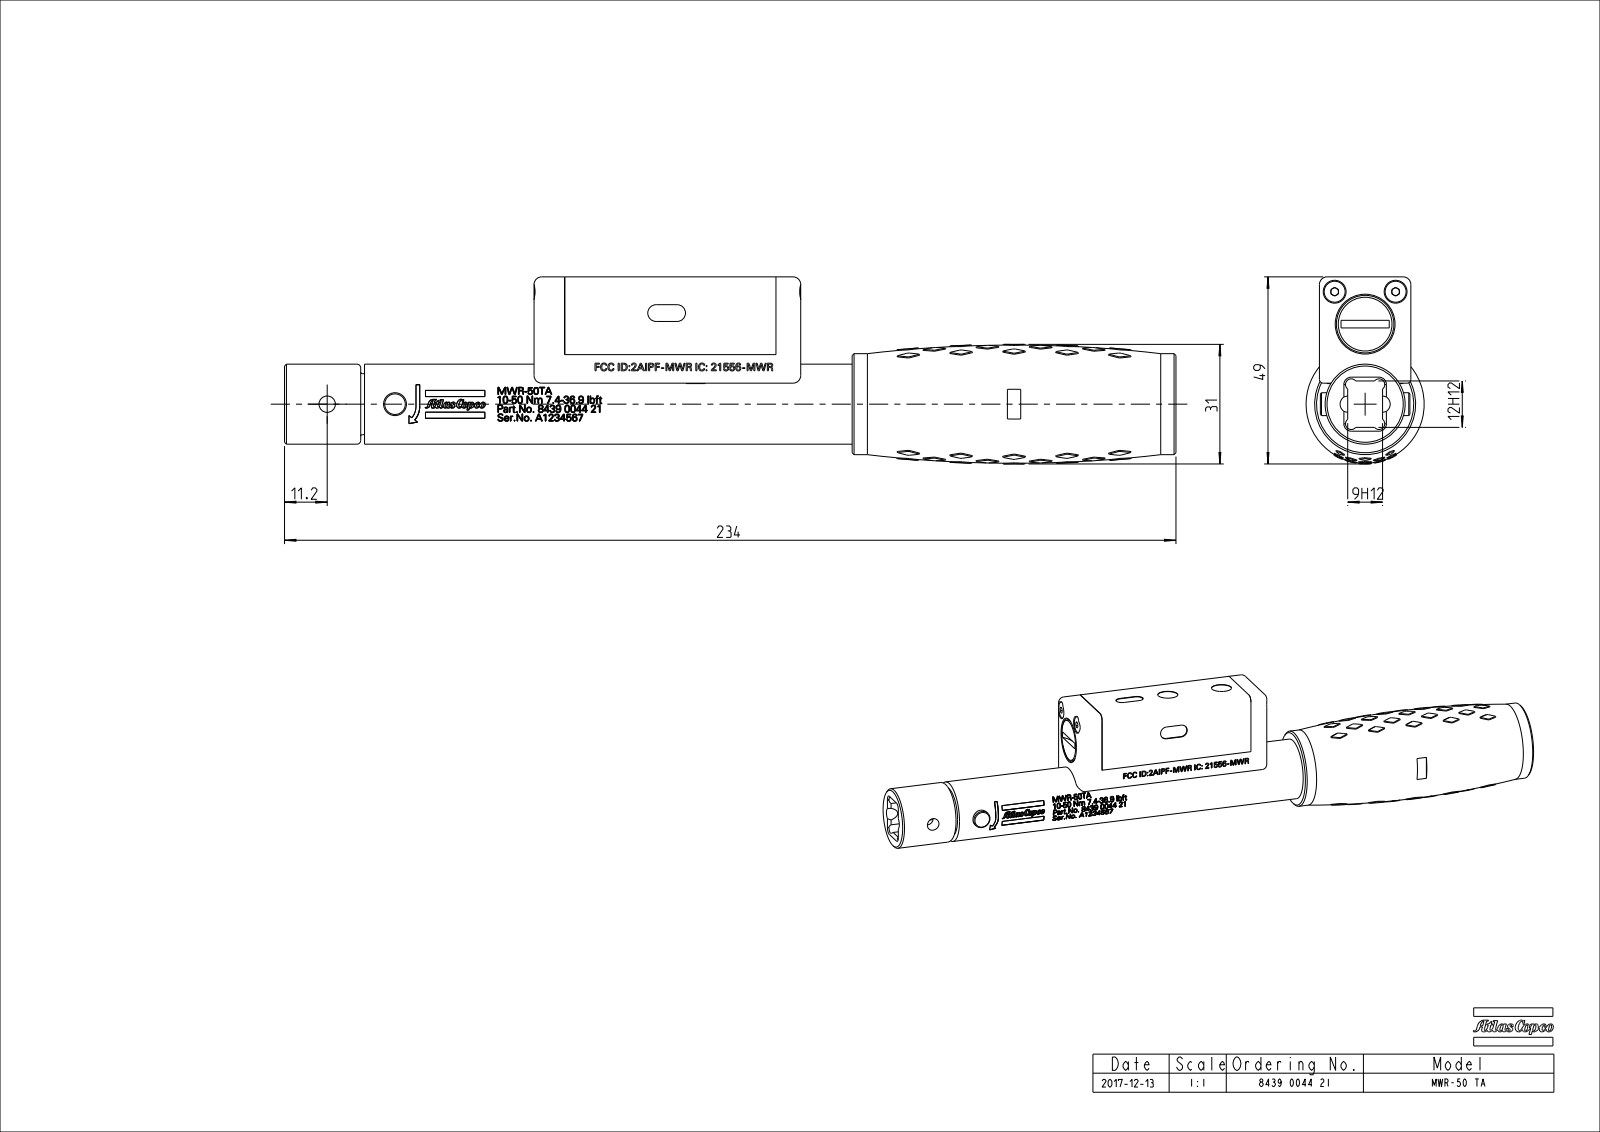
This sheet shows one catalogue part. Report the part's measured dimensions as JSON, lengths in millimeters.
{"part_name": "8439004421", "step_written_by": "SolidWorks 2016 (AUTOMOTIVE_DESIGN)", "units": "millimeters", "bodies": {"solids": 0, "faces": 555, "planar": 80, "cylindrical": 81, "other": 394}, "overall_size": [234, 49.21, 31], "round_holes": [[6, 2], [7, 2], [4.3, 1], [10.5, 1], [15.1, 1], [16.7, 1], [26.5, 1]], "round_bosses_or_shafts": [[5.5, 2], [21, 1], [14.1, 1], [6, 1]], "partial_cylinders_radius": [[2, 9], [0.4, 4], [0.5, 4], [2.25, 4], [1, 2], [2.5, 2], [11, 1]], "face_to_face_distances": [24, 16.5, 7.5, 61.9, 27.9, 62, 8, 160.5, 160.4, 98.5], "hole_center_spacings": [11.67, 30.57, 16, 20, 21]}
